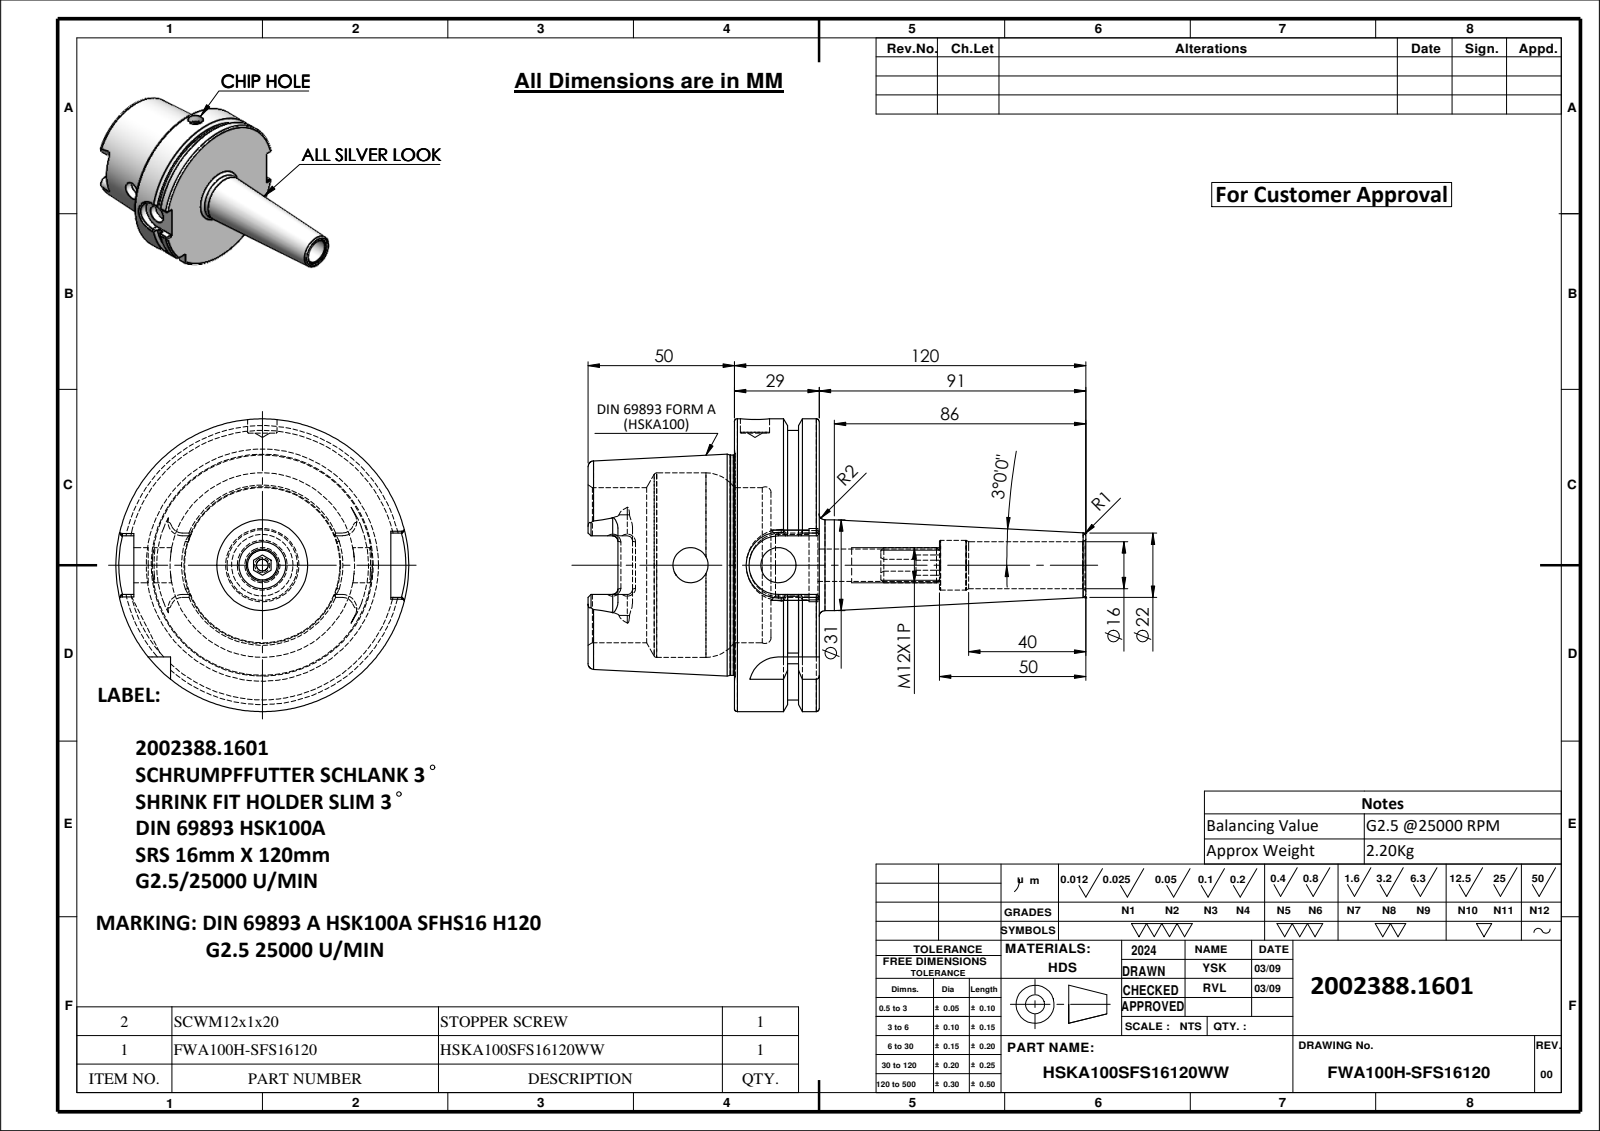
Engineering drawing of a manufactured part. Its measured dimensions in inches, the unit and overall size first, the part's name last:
Units: inches
Overall size (bounding box): 6.693 × 3.937 × 3.937
Round holes (diameter × count): ⌀0.472 ×2, ⌀0.157 ×1, ⌀0.394 ×1, ⌀0.433 ×1, ⌀0.63 ×1, ⌀0.669 ×1, ⌀0.827 ×1, ⌀0.984 ×1, ⌀2.087 ×1, ⌀2.48 ×1
Round bosses / shafts (diameter × count): ⌀3.937 ×1, ⌀3.622 ×1, ⌀2.959 ×1, ⌀1.22 ×1, ⌀0.472 ×1
Partial cylindrical surfaces — rounded edges, fillets, slot ends (radius × count): R0.071 ×6, R0.192 ×4, R0.394 ×2, R0.433 ×1
Main face-to-face distances: 1.14, 0.492, 0.648, 1.969, 2.461, 3.108, 2.83, 0.861, 0.369, 0.279
Hole centre spacings: 1.181
Volume: 17.88 in³ · Surface area: 96.23 in²
Bodies: 2 solids, 201 faces (61 planar, 56 cylindrical, 84 other)
Part name (STEP PRODUCT): HSKA100SFS16120WW; FWA100H-SFS16120; SCWM12X1P
STEP written by: SolidWorks 2024 (AUTOMOTIVE_DESIGN)
